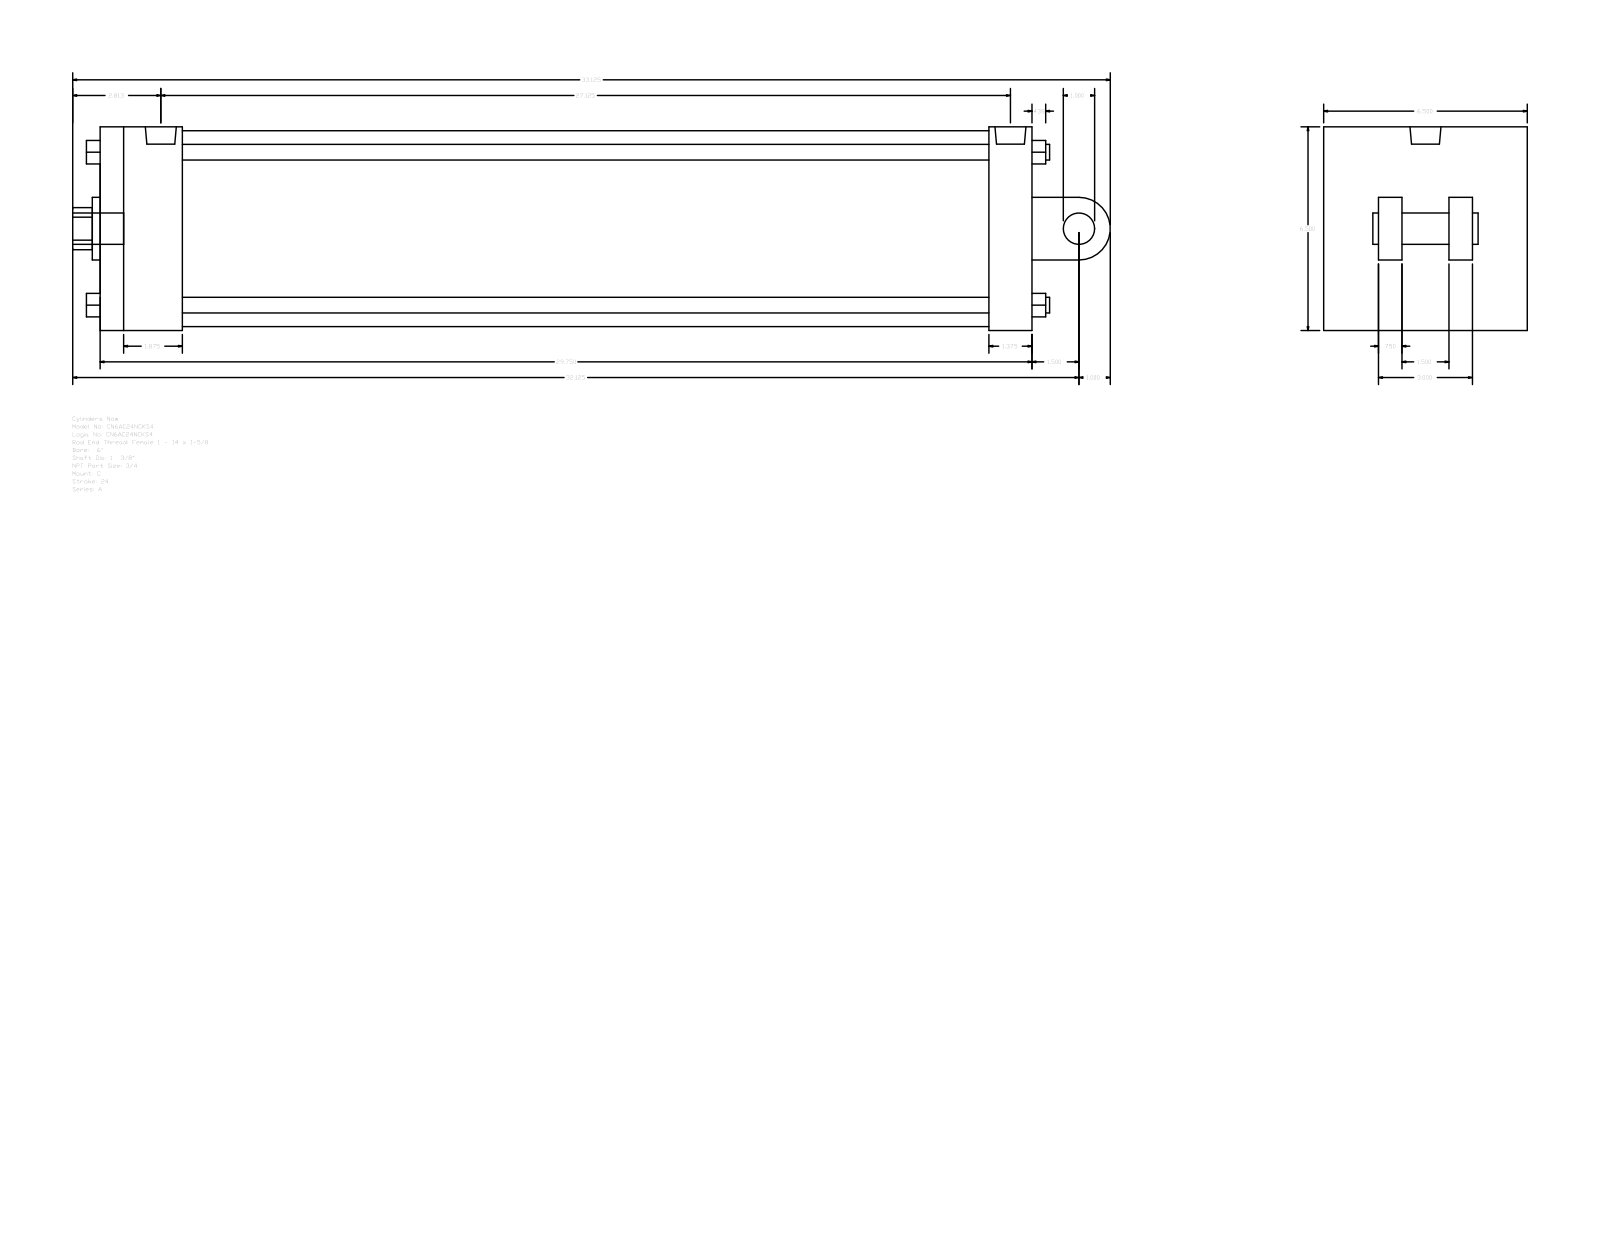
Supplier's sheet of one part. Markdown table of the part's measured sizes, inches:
| quantity | value |
| --- | --- |
| part name | A_C__0600_1.375 |
| STEP written by | GSSL Pune (CONFIG_CONTROL_DESIGN) |
| units | inches |
| bodies | 0 solids, 135 faces (102 planar, 33 cylindrical, 0 other) |
| overall size | 33.125 × 6.5 × 6.5 |
| round holes (diameter × count) | 0.594 × 2, 0.989 × 1, 1.375 × 1, 2 × 1, 6.25 × 1 |
| round bosses / shafts (diameter × count) | 0.5 × 4, 1 × 2, 0.594 × 2, 0.989 × 1 |
| partial cylindrical surfaces (radius × count) | 0.672 × 1, 1 × 1 |
| main face-to-face distances | 6.5, 29.75, 0.75, 2.25, 2.625, 27.125, 28.375, 25.75, 1.375, 1.75 |
| hole center spacings | 0.219 |
